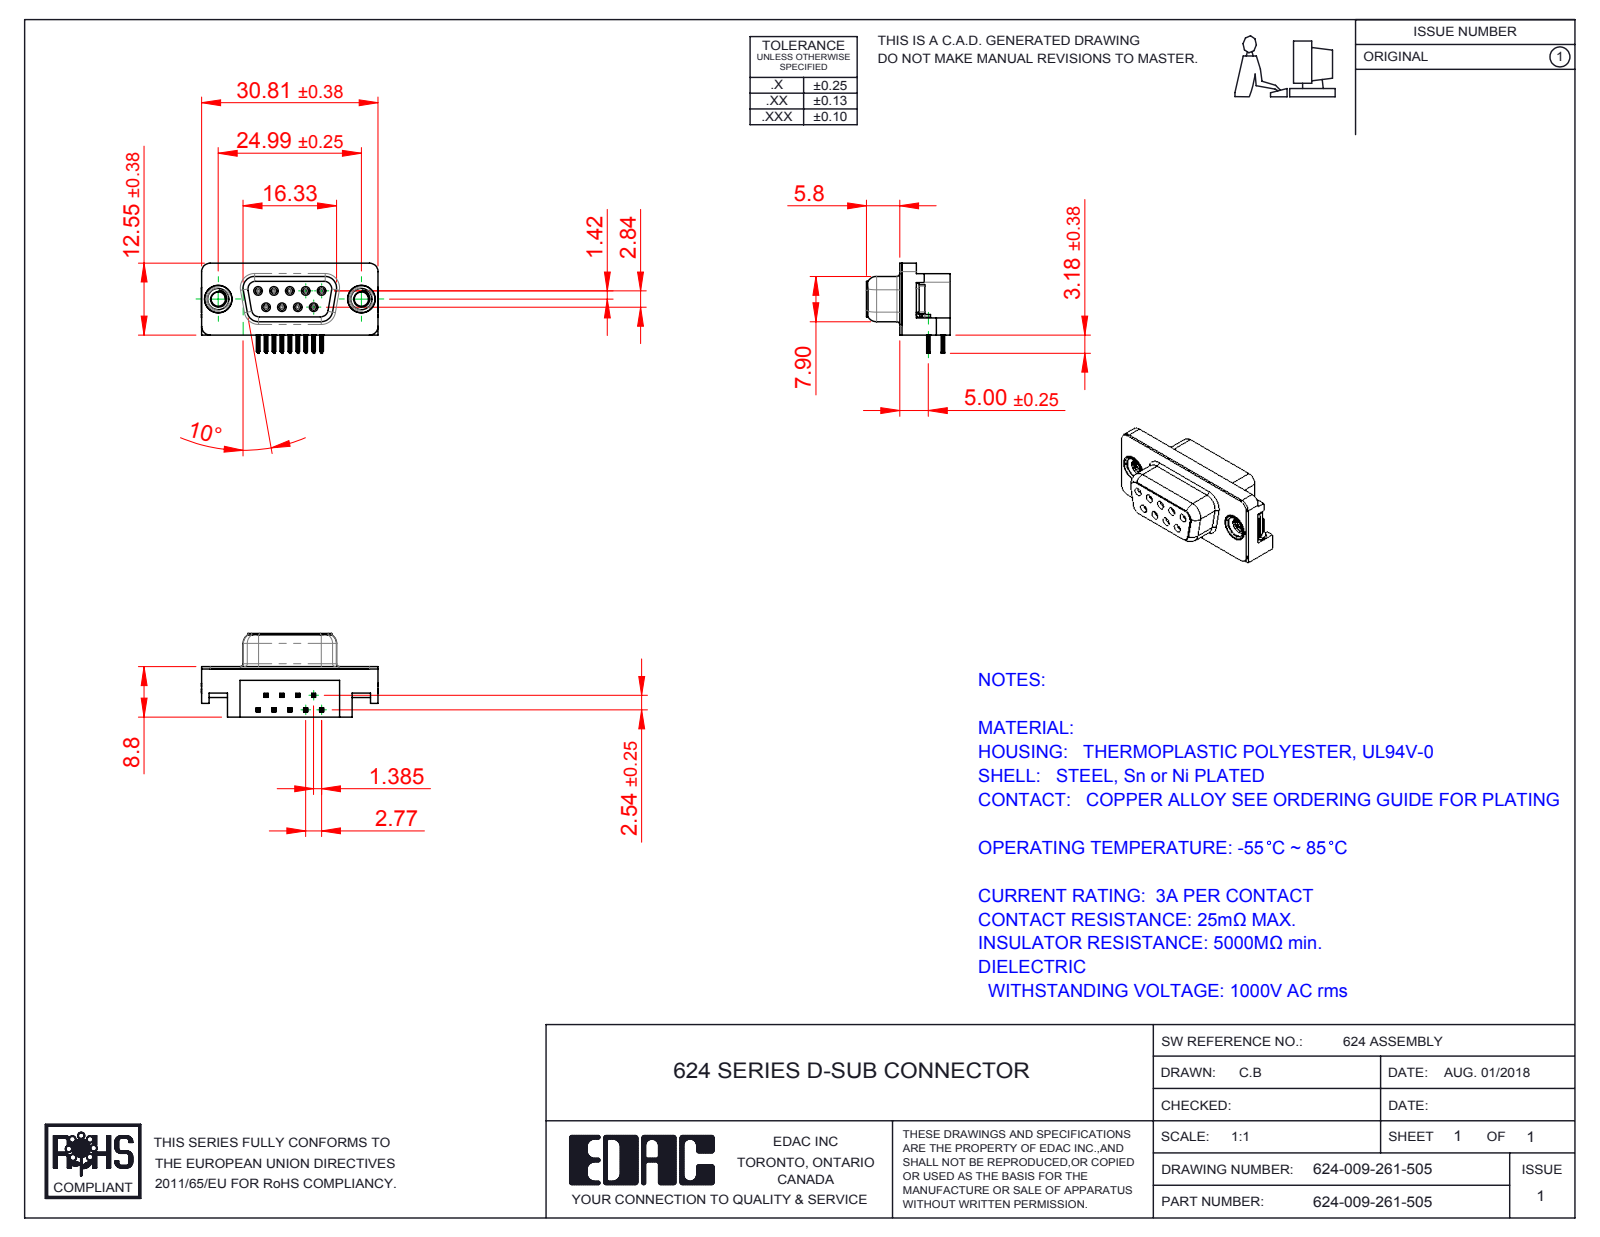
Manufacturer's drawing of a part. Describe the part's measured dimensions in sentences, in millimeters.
The part is named "624-009-261-505; 624 M3 Threaded Rivet; 624 Non Board Mount; 624 Contact Top (+3 more)". Its 3-D file was written by "SolidWorks 2016 (CONFIG_CONTROL_DESIGN)". It is 15 solids with 1520 faces: 642 planar, 410 cylindrical and 468 other. Overall it measures 30.89 by 15.73 by 14.6 millimeters. Its volume is 2 932 cubic millimeters and its surface area 4 338 square millimeters. Round holes: 9 of diameter 0.8, 9 of diameter 0.9, 2 of diameter 2.5, 2 of diameter 4, 2 of diameter 4.8, 2 of diameter 5. Round bosses or shafts: 9 of diameter 1.2, 2 of diameter 4.9, 2 of diameter 4.75, 2 of diameter 3.9. Partial cylindrical surfaces (rounded edges, fillets, slot ends): 72 of radius 0.1, 36 of radius 0.15, 18 of radius 0.35, 18 of radius 1, 9 of radius 0.34, 8 of radius 0.25, 8 of radius 1.35, 7 of radius 1.5. The main face-to-face distances are 0.4, 8.4, 8.8, 2.9, 2.5, 6.2, 5.9, 0.35, 10.69, 10.34. The hole center spacings are 3.16, 2.77, 5.54, 5.03, 5.04, 8.31, 7.48, 7.49.
